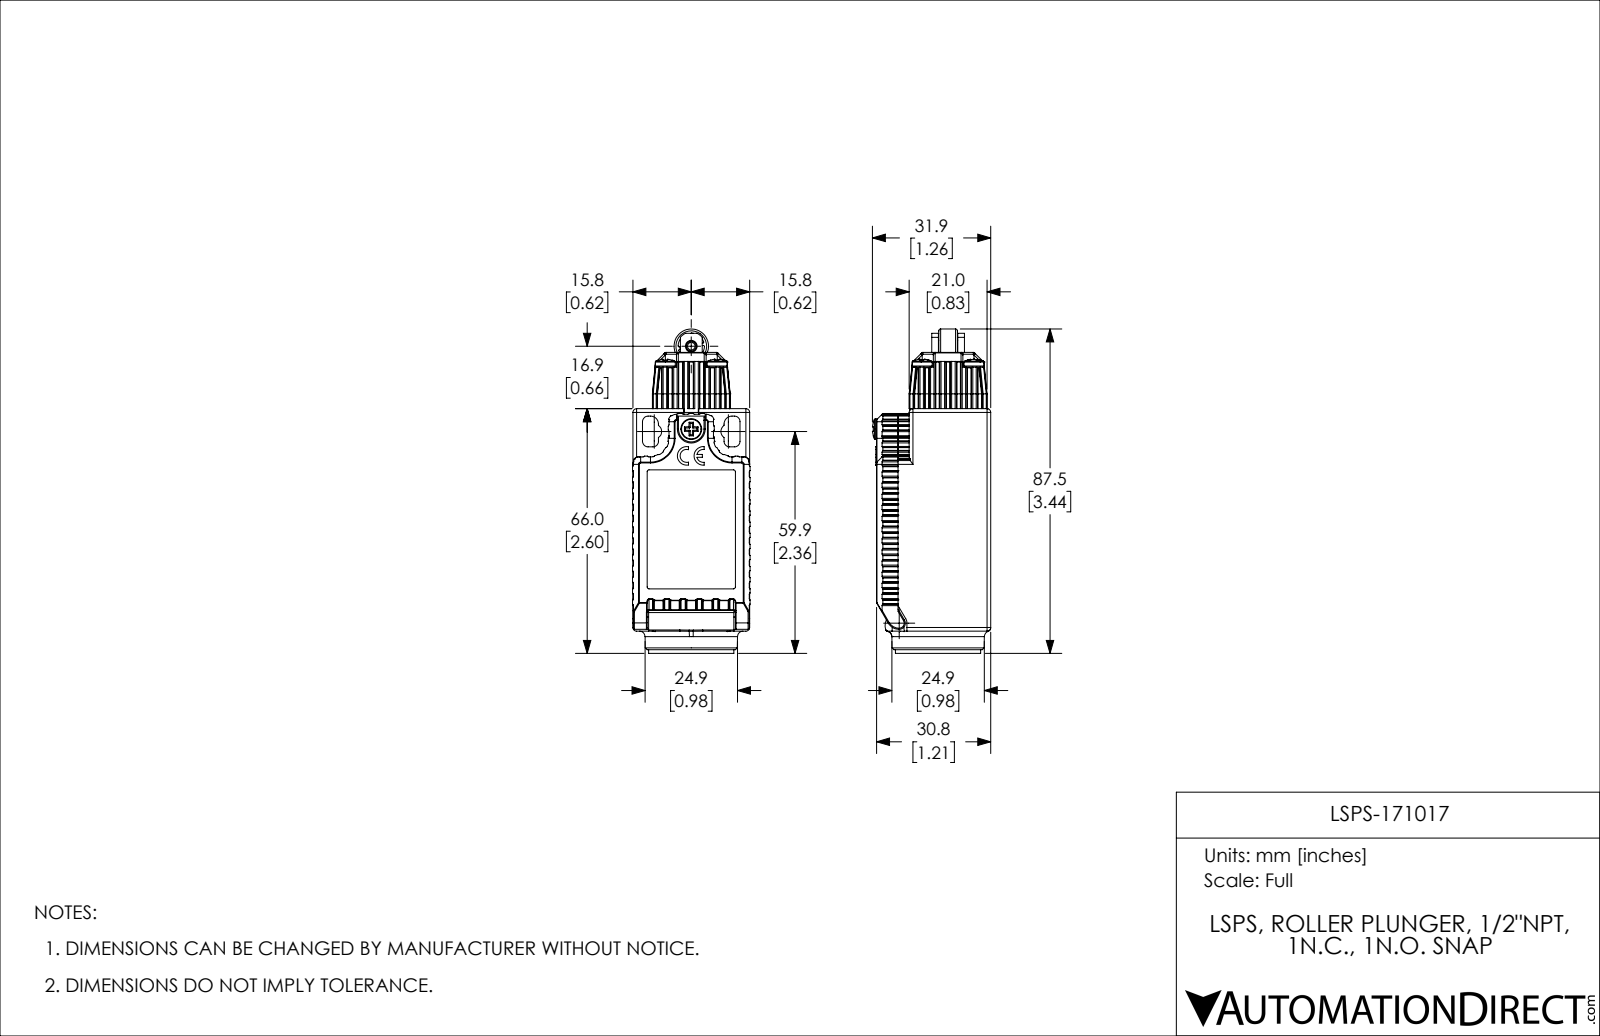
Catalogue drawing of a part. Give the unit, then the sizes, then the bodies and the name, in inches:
Units: inches
Overall size (bounding box): 3.445 × 1.257 × 1.248
Round holes (diameter × count): ⌀0.091 ×5, ⌀0.102 ×4, ⌀0.126 ×4, ⌀0.217 ×4, ⌀0.157 ×2, ⌀0.081 ×1, ⌀0.098 ×1, ⌀0.124 ×1, ⌀0.134 ×1, ⌀0.146 ×1, ⌀0.197 ×1, ⌀0.244 ×1
Round bosses / shafts (diameter × count): ⌀0.067 ×5, ⌀0.213 ×4, ⌀0.098 ×4, ⌀0.906 ×1, ⌀0.717 ×1, ⌀0.618 ×1, ⌀0.61 ×1, ⌀0.441 ×1
Partial cylindrical surfaces — rounded edges, fillets, slot ends (radius × count): R0.02 ×253, R0.008 ×132, R0.004 ×92, R0.012 ×61, R0.013 ×32, R0.039 ×23, R0.079 ×14, R0.024 ×9
Main face-to-face distances: 0.089, 1.152, 1.24, 0.063, 1.102, 0.039, 0.102, 1.063, 0.22, 1.165
Hole centre spacings: 0.39, 0.551, 0.306, 0.324, 0.471, 0.646, 0.78, 0.787
Volume: 1.761 in³ · Surface area: 45.94 in²
Bodies: 15 solids, 2867 faces (1314 planar, 1176 cylindrical, 377 other)
Part name (STEP PRODUCT): LSPS-171017
STEP written by: SolidWorks 2017 (AUTOMOTIVE_DESIGN)
